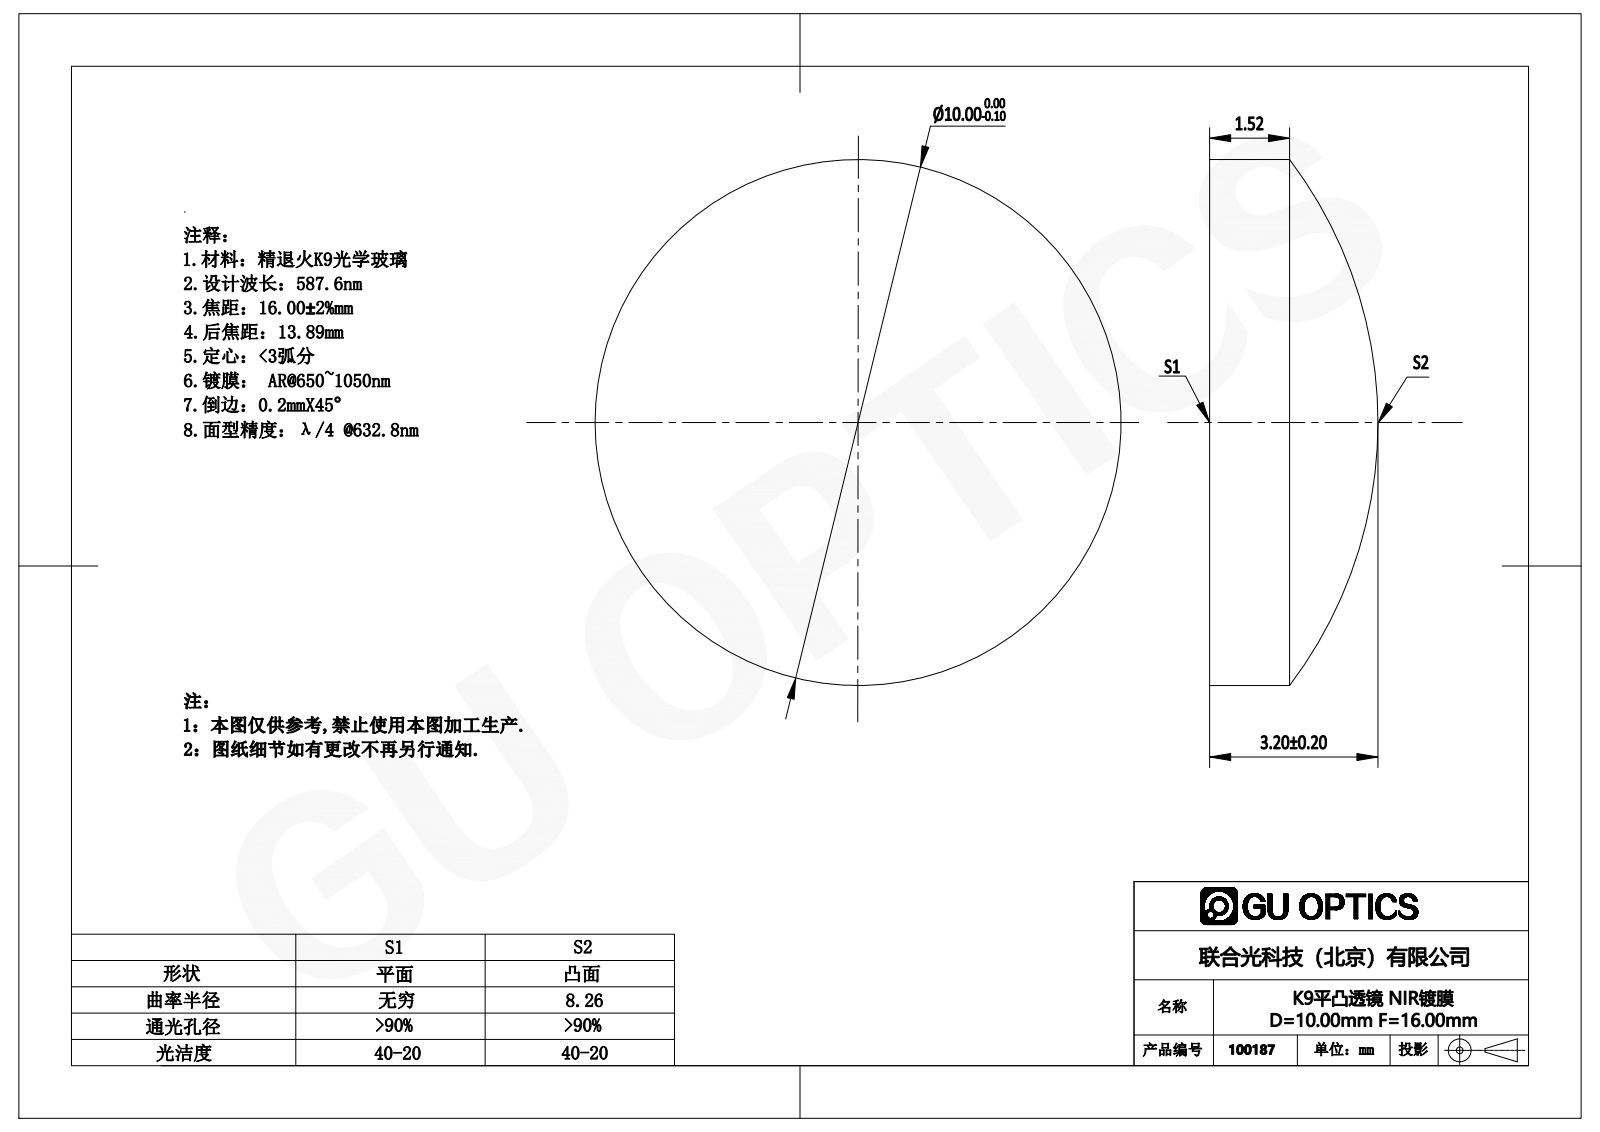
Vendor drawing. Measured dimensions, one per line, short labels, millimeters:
name: 100187
written by: SolidWorks 2016 (AUTOMOTIVE_DESIGN)
unit: mm
bodies: 1 solid, 5 faces (1 planar, 2 cylindrical, 2 other)
size: 10 × 10 × 3.2
volume: 188 mm³; area: 214 mm²
bosses: 1× ⌀10
